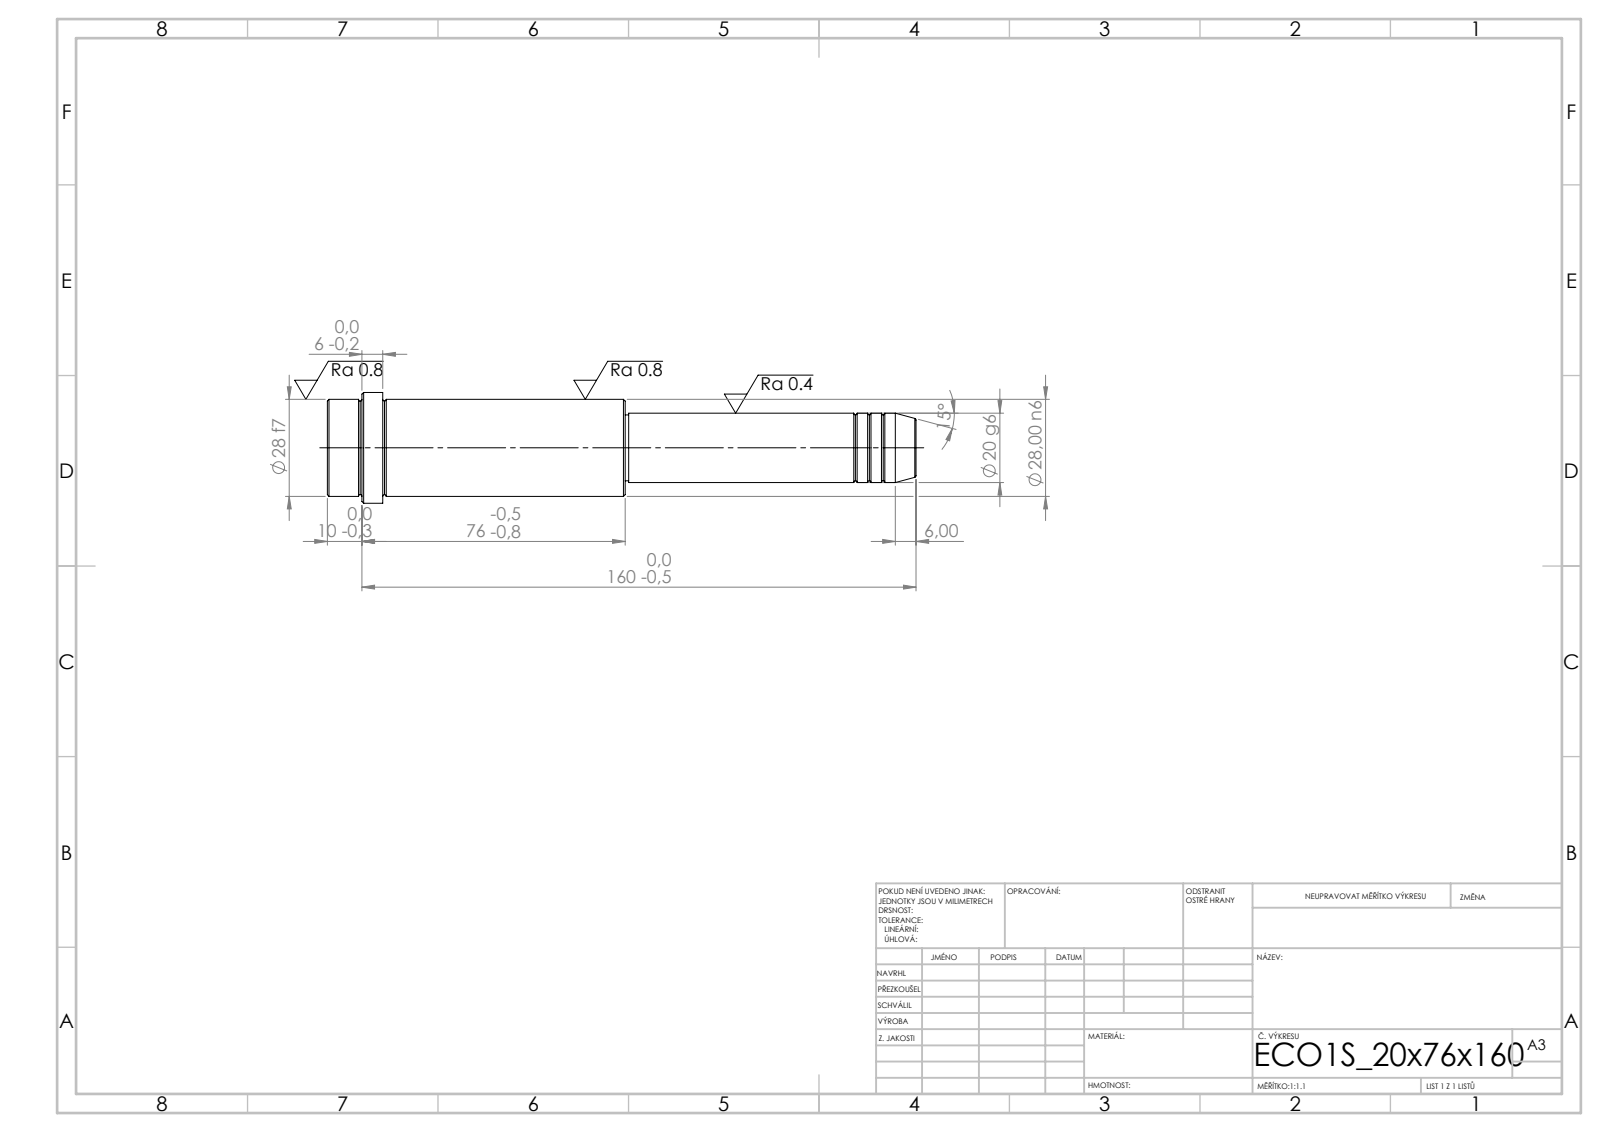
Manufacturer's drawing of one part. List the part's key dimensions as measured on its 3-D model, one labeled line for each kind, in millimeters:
STEP written by: SolidWorks 2019 (CONFIG_CONTROL_DESIGN)
Units: millimetres
Bodies: 1 solid, 52 faces (6 planar, 16 cylindrical, 30 other)
Overall size (bounding box): 170 × 32 × 32
Volume: 79 981 mm³ · Surface area: 14 578 mm²
Round bosses / shafts (diameter × count): ⌀32 ×1, ⌀28 ×1, ⌀20 ×1, ⌀19 ×1
Main face-to-face distances: 86, 84, 170, 154, 70, 16, 160, 76, 6, 10
